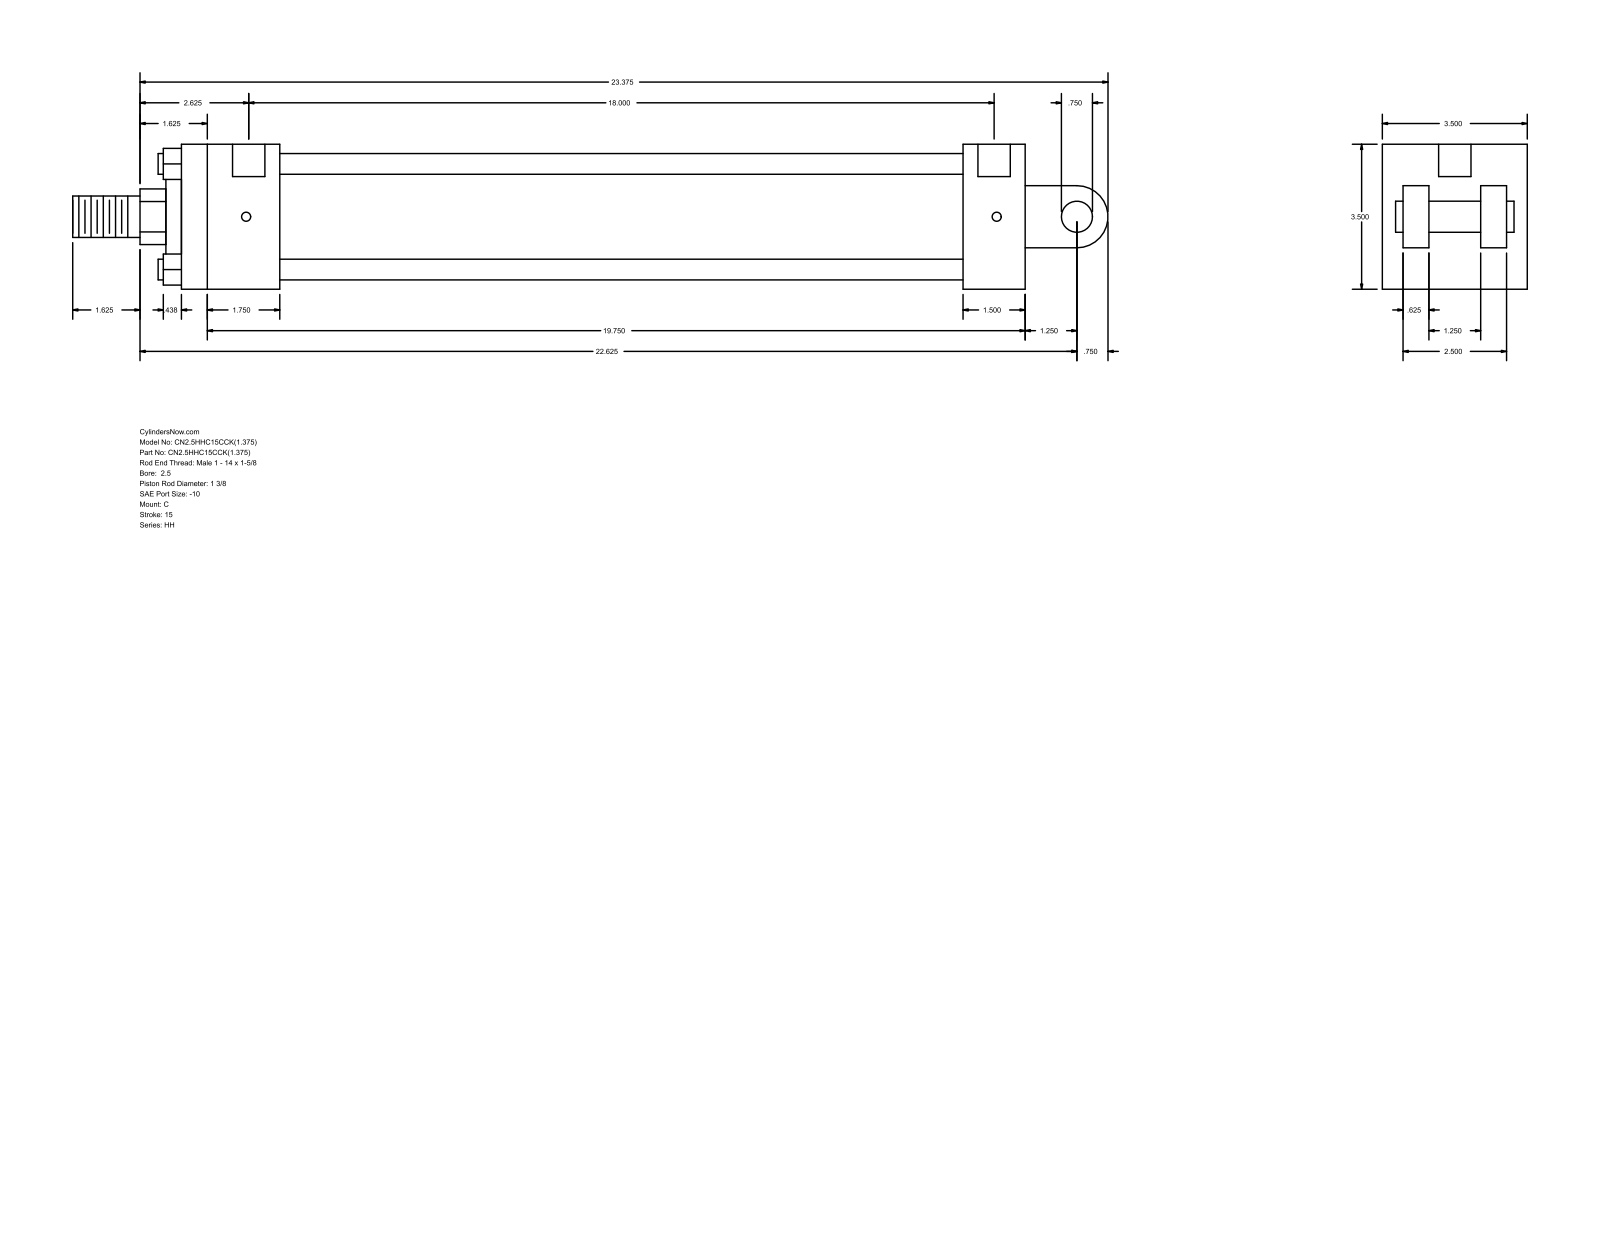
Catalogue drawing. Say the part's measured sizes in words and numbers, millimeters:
The part is named "HH_C__0250_1.375". Its 3-D file was written by "GSSL Pune (CONFIG_CONTROL_DESIGN)". It is 0 solids with 99 faces: 70 planar, 29 cylindrical and 0 other. Overall it measures 635 by 88.9 by 88.9 millimeters. Round holes: 4 of diameter 5.56, 2 of diameter 19.84. Round bosses or shafts: 4 of diameter 12.7, 1 of diameter 73.03, 1 of diameter 50.8, 1 of diameter 34.92, 1 of diameter 25.4, 1 of diameter 19.05. Partial cylindrical surfaces (rounded edges, fillets, slot ends): 1 of radius 17.06, 1 of radius 19.05. The main face-to-face distances are 88.9, 517.52, 38.1, 63.5, 12.7, 479.42, 60.32, 419.1, 457.2, 28.57. The hole center spacings are 1.58, 458.79, 460.37, 457.21.
